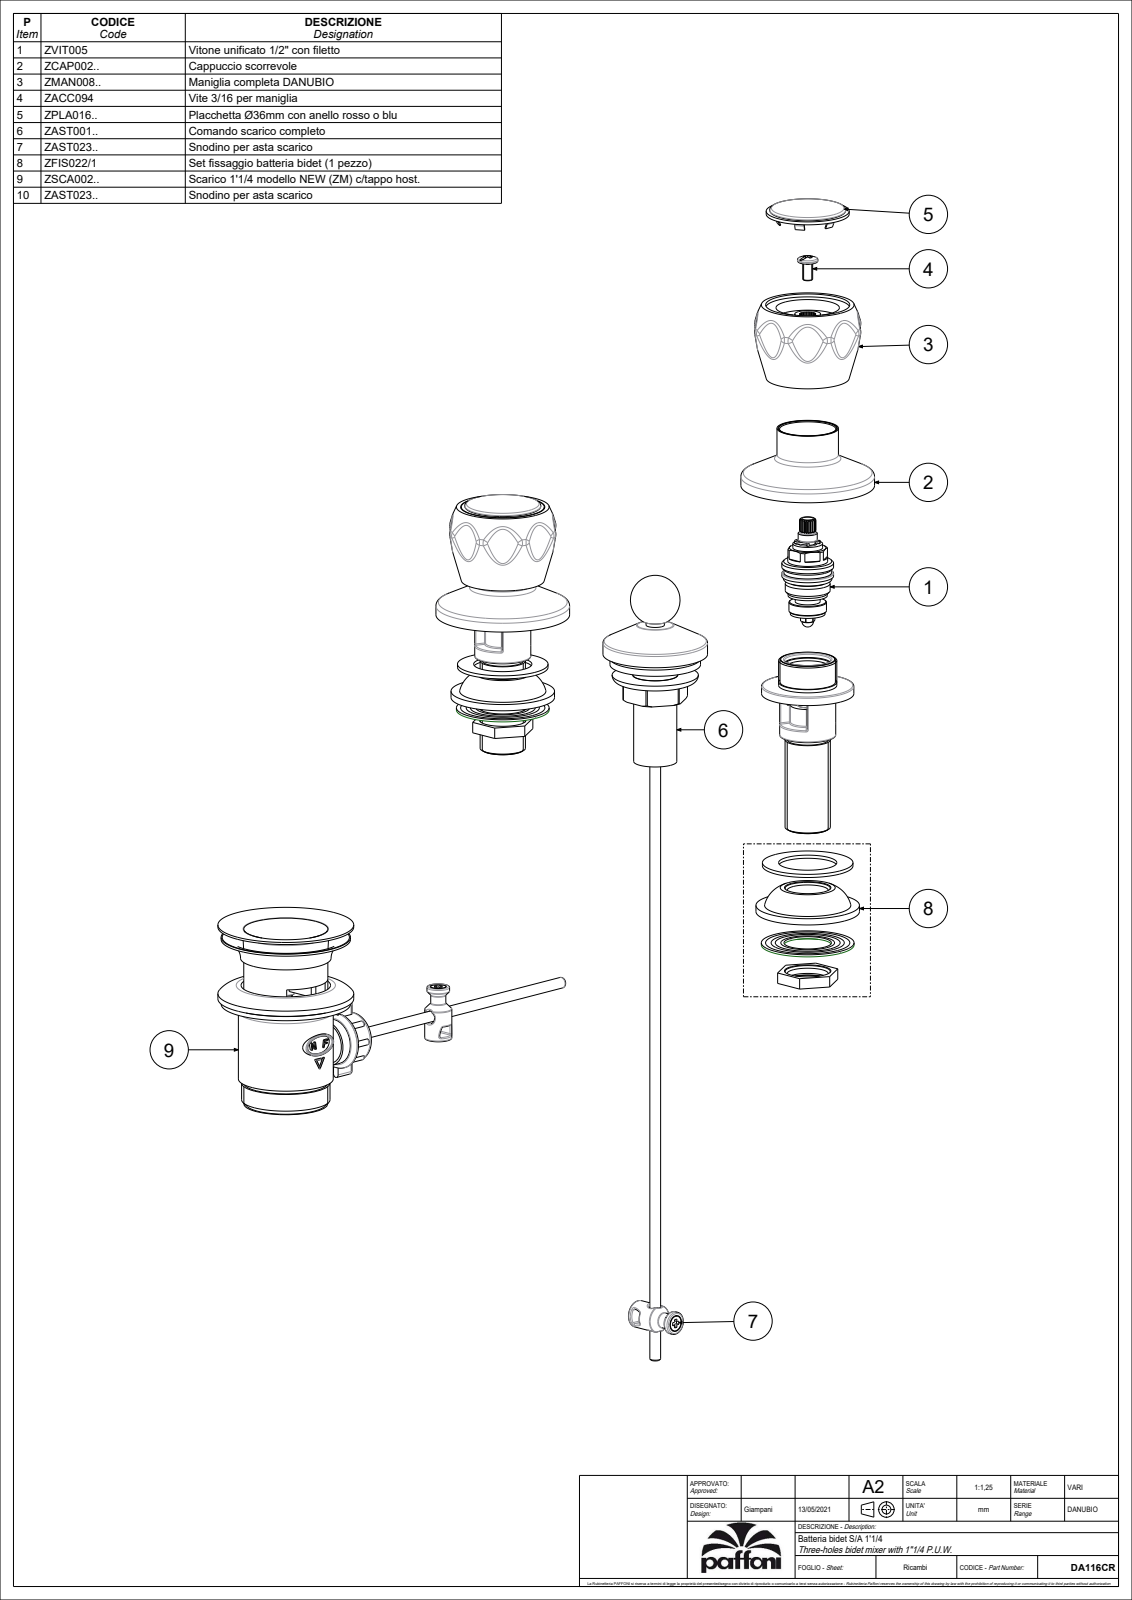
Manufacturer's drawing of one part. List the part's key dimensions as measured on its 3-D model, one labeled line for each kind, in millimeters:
Part name (STEP PRODUCT): DA116CR
STEP written by: CREO PARAMETRIC BY PTC INC, 2020044 (CONFIG_CONTROL_DESIGN)
Units: millimetres
Bodies: 3 solids, 173 faces (11 planar, 32 cylindrical, 130 other)
Overall size (bounding box): 262 × 62 × 53.5
Volume: 207 173 mm³ · Surface area: 35 023 mm²
Round bosses / shafts (diameter × count): ⌀62 ×2, ⌀38.5 ×2, ⌀28.5 ×2, ⌀48.5 ×1, ⌀8 ×1
Partial cylindrical surfaces — rounded edges, fillets, slot ends (radius × count): R21.31 ×16
Main face-to-face distances: 14.8, 50.1, 35.3, 50.5, 35.7, 0.4, 14, 0.8, 36.1, 36.5
